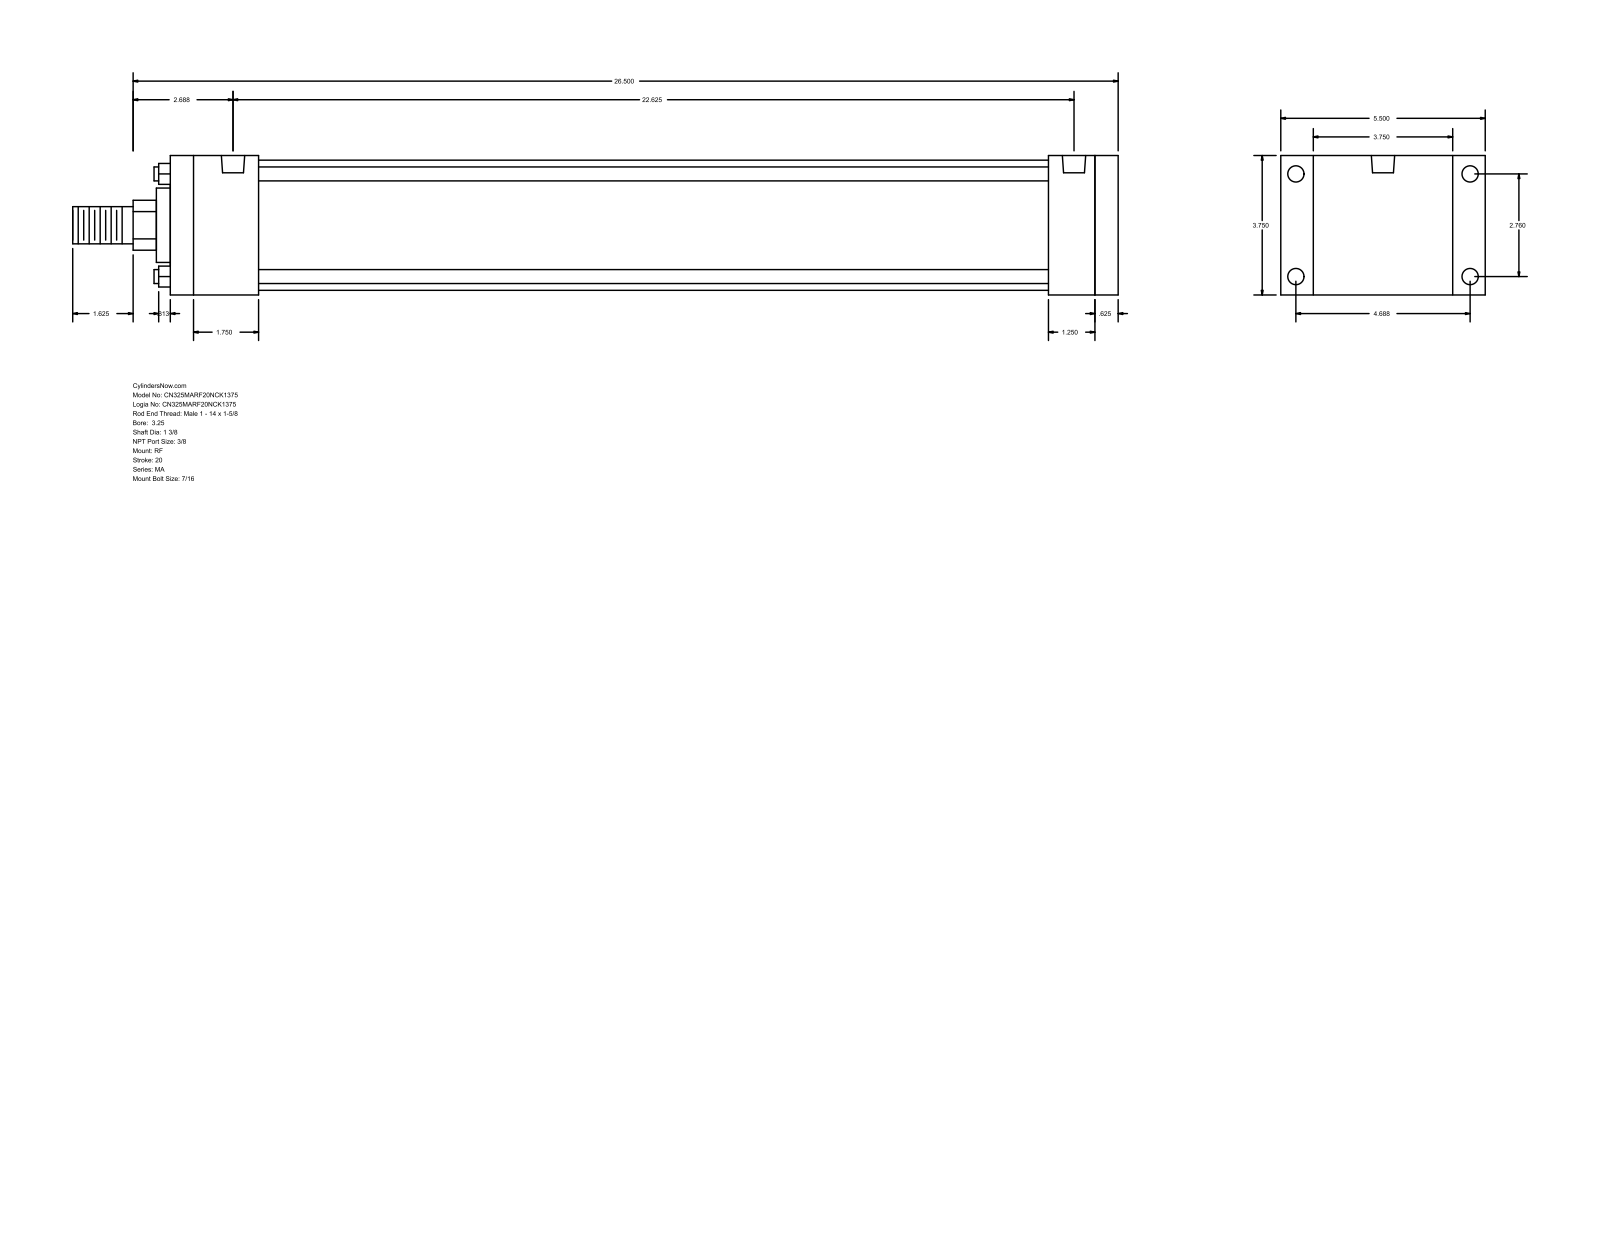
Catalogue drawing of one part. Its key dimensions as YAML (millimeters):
part_name: "MA_RF__0325_1.375"
step_written_by: "GSSL Pune (CONFIG_CONTROL_DESIGN)"
units: millimeters
bodies: {solids: 0, faces: 92, planar: 64, cylindrical: 28, other: 0}
overall_size: [714.38, 139.7, 95.25]
round_holes:
  - {diameter: 11.11, count: 8}
  - {diameter: 15.93, count: 2}
round_bosses_or_shafts:
  - {diameter: 9.53, count: 4}
  - {diameter: 88.9, count: 1}
  - {diameter: 50.8, count: 1}
  - {diameter: 34.92, count: 1}
  - {diameter: 25.4, count: 1}
partial_cylinders:
  - {radius: 17.06, count: 1}
face_to_face_distances: [95.24, 647.7, 631.83, 15.87, 22.23, 117.47, 600.08, 31.75, 47.62, 60.32]
hole_center_spacings: [4.77, 70.1, 119.06, 138.16, 565.14, 569.91, 574.68]
